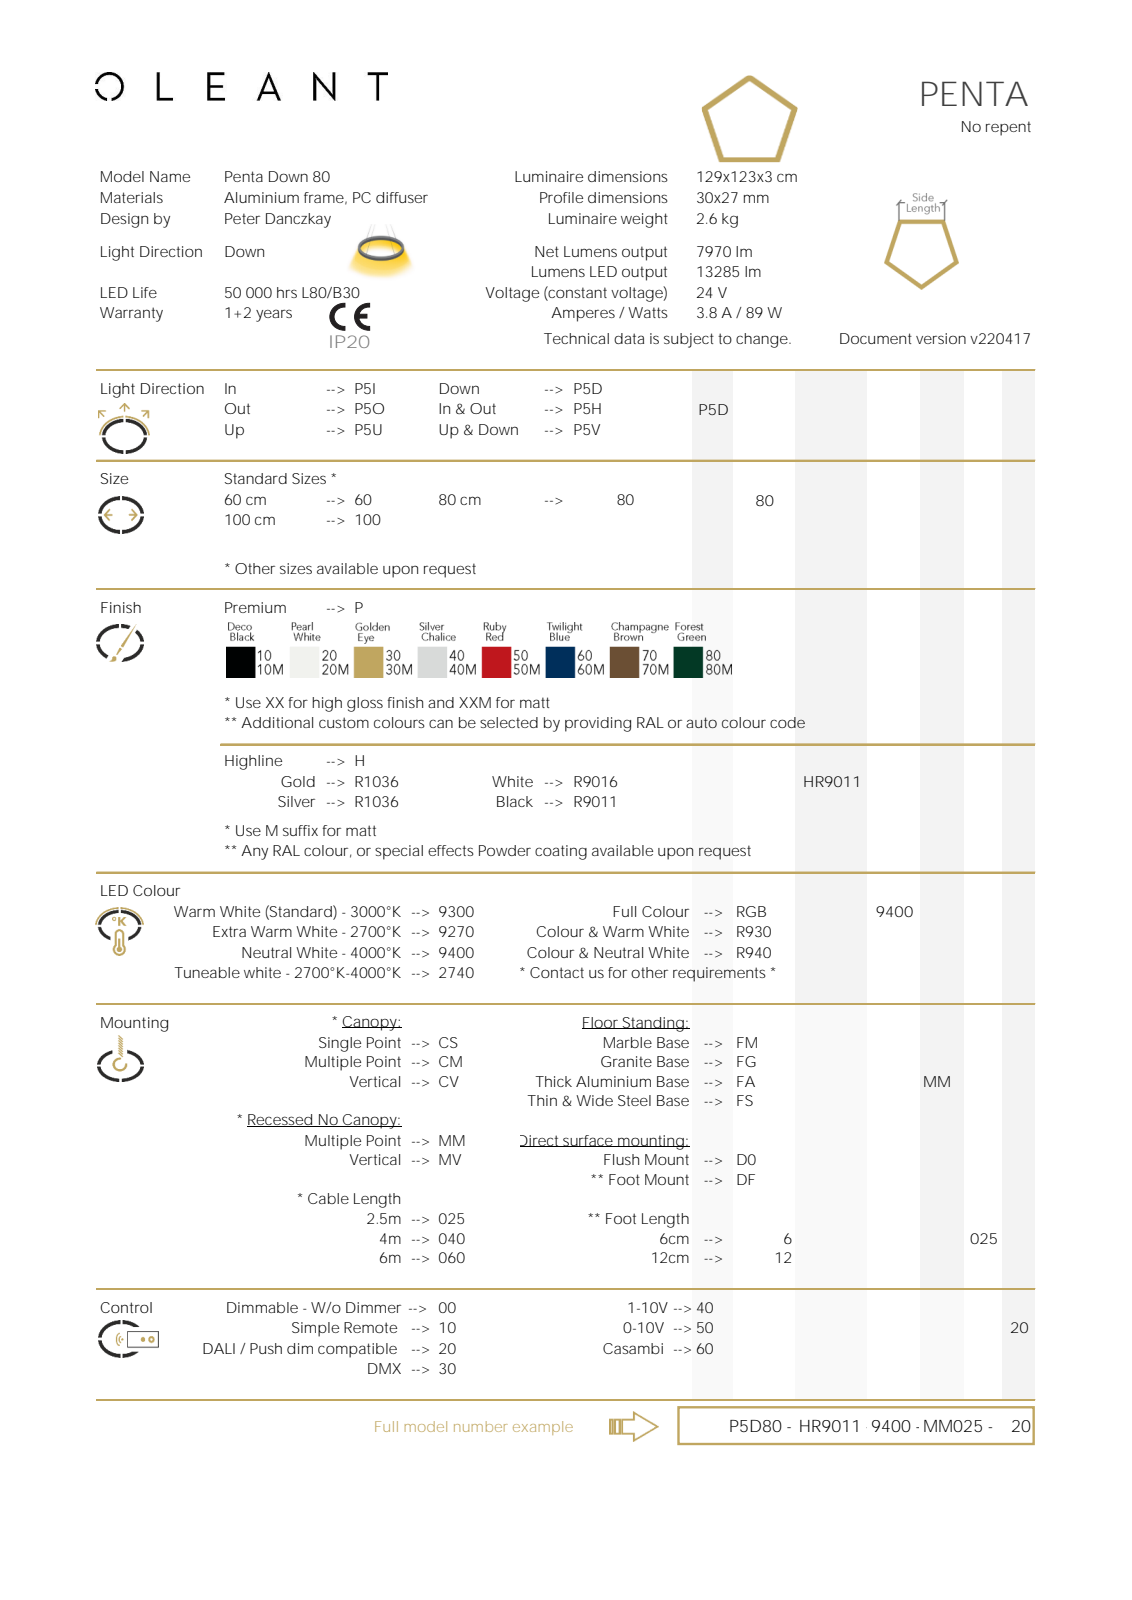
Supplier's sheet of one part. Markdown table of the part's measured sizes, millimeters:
| quantity | value |
| --- | --- |
| part name | eclipse; frame; plexi; cable (+1 more) |
| STEP written by | Autodesk Inventor 2020 (AUTOMOTIVE_DESIGN) |
| units | millimeters |
| bodies | 8 solids, 136 faces (95 planar, 35 cylindrical, 6 other) |
| overall size | 1294.43 × 1231.07 × 1049.5 |
| volume | 2 994 000 mm³ |
| surface area | 1 023 000 mm² |
| round holes (diameter × count) | 3 × 3 |
| round bosses / shafts (diameter × count) | 11 × 3, 9 × 3, 4 × 3, 1.2 × 3 |
| partial cylindrical surfaces (radius × count) | 0.75 × 20 |
| main face-to-face distances | 2, 28, 26, 24.5, 22.5, 30, 28.01, 28.15, 27.86, 25.86 |
| hole center spacings | 1259.16, 778.2 |
